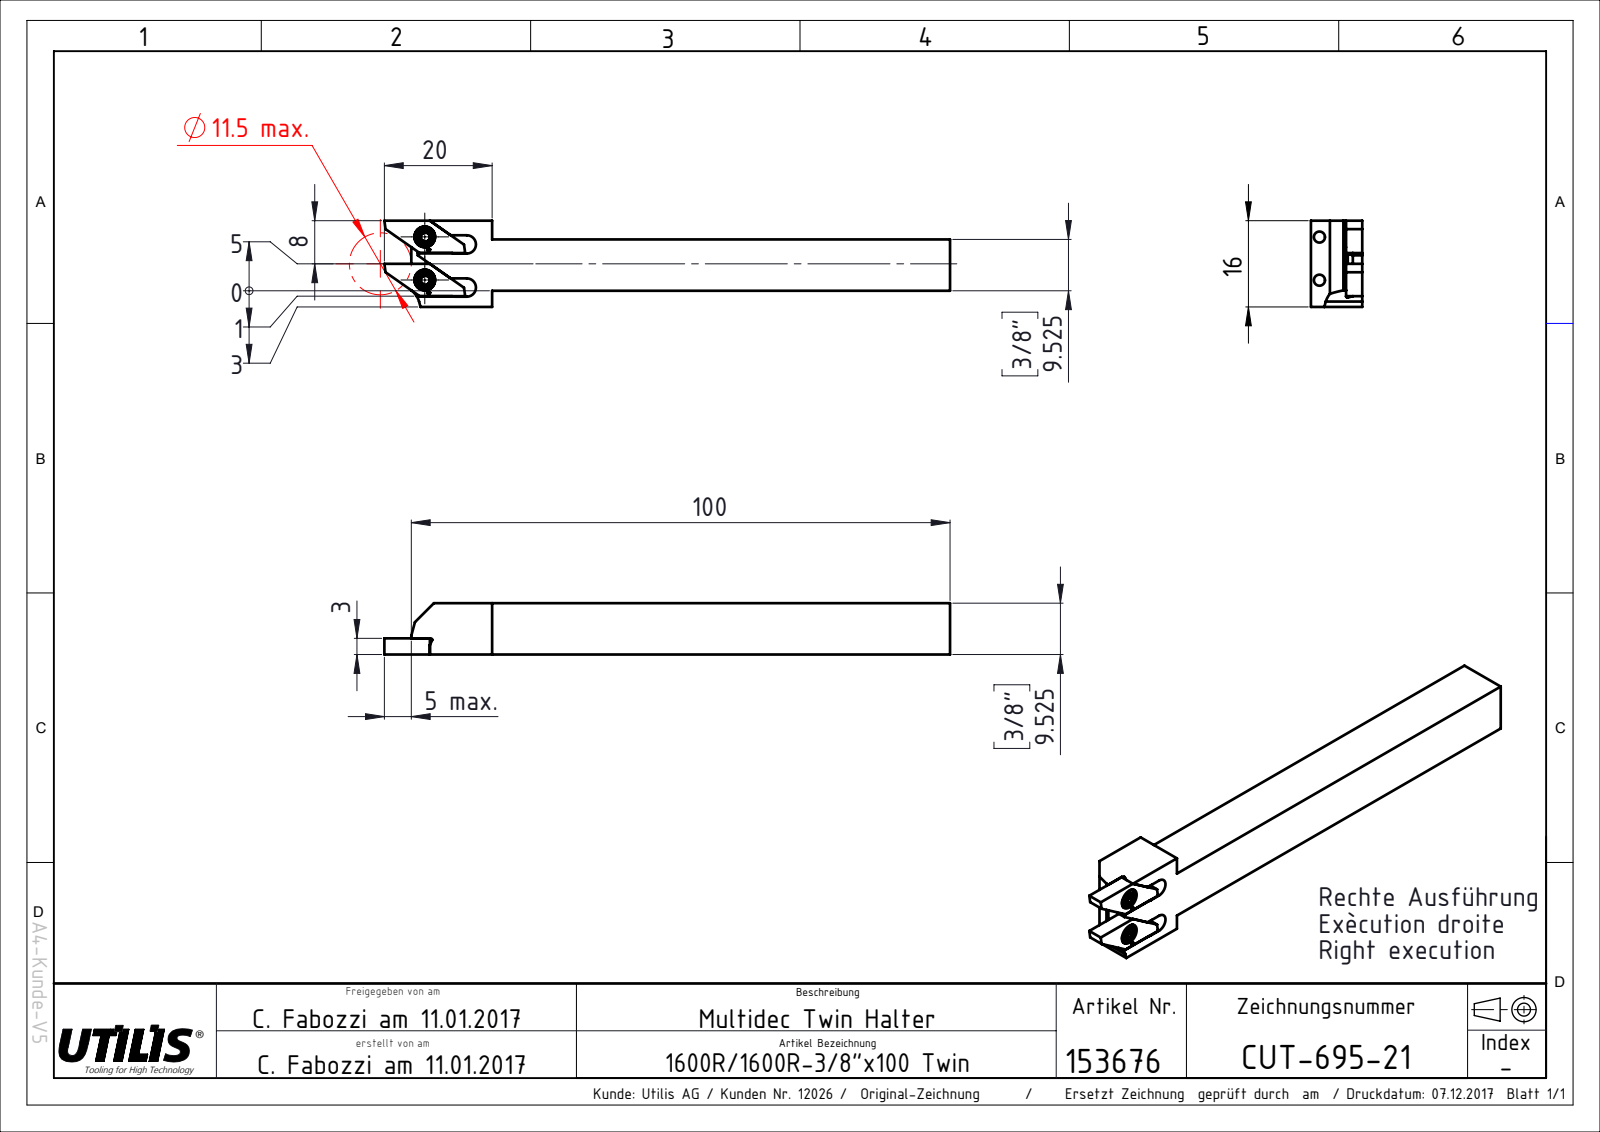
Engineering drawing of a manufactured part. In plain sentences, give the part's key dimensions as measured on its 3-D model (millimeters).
The part is named "CUT-695-21". Its 3-D file was written by "SolidWorks 2016 (AUTOMOTIVE_DESIGN)". It is 1 solid with 86 faces: 77 planar, 9 cylindrical and 0 other. Overall it measures 105 by 16 by 9.53 millimeters. Its volume is 9 851 cubic millimeters and its surface area 4 471 square millimeters. Partial cylindrical surfaces (rounded edges, fillets, slot ends): 2 of radius 0.5, 2 of radius 1.55, 2 of radius 1.7, 1 of radius 4.1. The main face-to-face distances are 9.53, 9.52, 3, 13, 3.48, 12.52, 16, 8, 85, 6.53.
